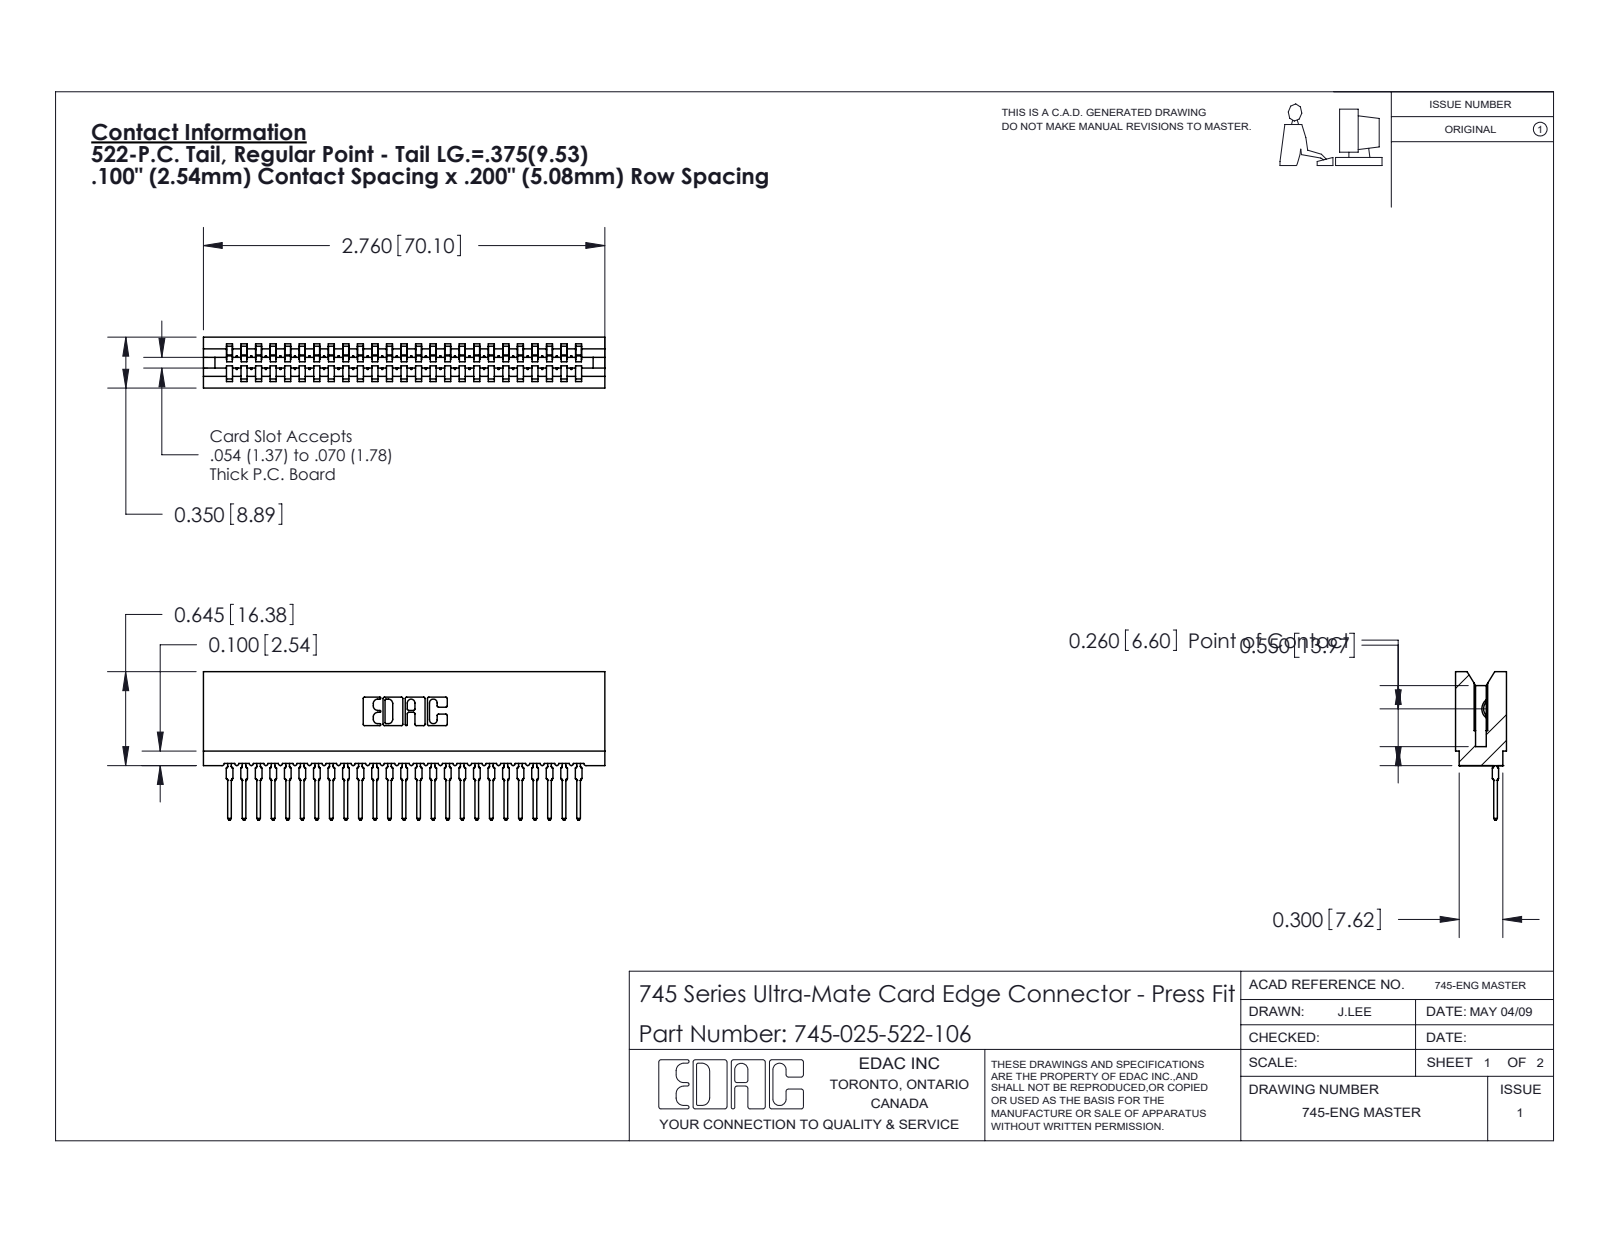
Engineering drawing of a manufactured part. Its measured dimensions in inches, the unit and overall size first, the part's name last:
Units: inches
Overall size (bounding box): 2.76 × 1.021 × 0.35
Partial cylindrical surfaces — rounded edges, fillets, slot ends (radius × count): R0.015 ×50, R0.021 ×50, R0.01 ×22, R0.007 ×6, R0.031 ×6, R0.005 ×4, R0.011 ×4, R0.026 ×3
Main face-to-face distances: 0.1, 0.2, 0.35, 0.3, 0.4, 0.5, 0.138, 0.212, 0.045, 0.305
Volume: 0.377 in³ · Surface area: 17.45 in²
Bodies: 26 solids, 2896 faces (1731 planar, 515 cylindrical, 650 other)
Part name (STEP PRODUCT): 745-292-001_522; 745 Part_Insulator Option - 06; 745-025-522-106
STEP written by: SolidWorks 2020 (CONFIG_CONTROL_DESIGN)
